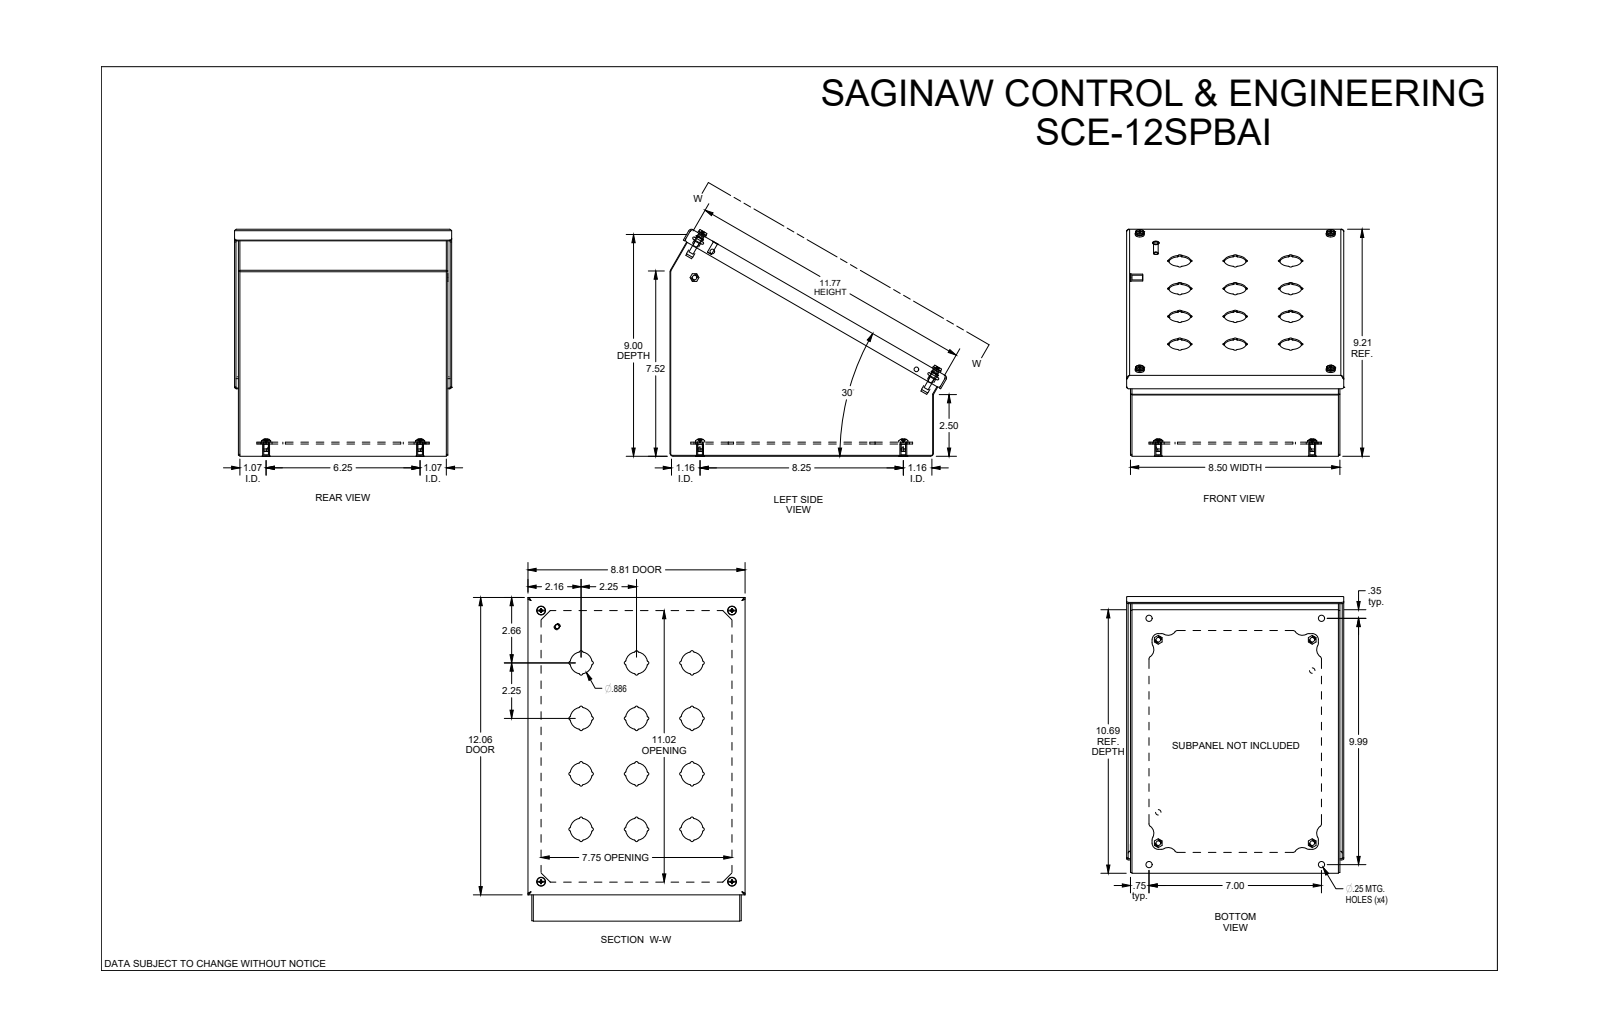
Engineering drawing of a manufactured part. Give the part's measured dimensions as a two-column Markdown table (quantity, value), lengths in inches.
| quantity | value |
| --- | --- |
| part name | SCE-12SPBAI |
| STEP written by | SolidWorks 2019 (AUTOMOTIVE_DESIGN) |
| units | inches |
| bodies | 20 solids, 765 faces (254 planar, 443 cylindrical, 68 other) |
| overall size | 11.245 × 9.233 × 8.813 |
| volume | 33.25 in³ |
| surface area | 1 091 in² |
| round holes (diameter × count) | 0.25 × 12, 0.19 × 9, 0.22 × 4, 0.266 × 4, 0.281 × 4, 0.317 × 4, 0.187 × 2, 0.218 × 2, 0.193 × 1 |
| round bosses / shafts (diameter × count) | 0.292 × 6, 0.28 × 5, 0.362 × 4, 0.34 × 4, 0.27 × 4, 0.26 × 4, 0.256 × 1, 0.188 × 1 |
| partial cylindrical surfaces (radius × count) | 0.04 × 105, 0.062 × 48, 0.03 × 14, 0.06 × 14, 0.25 × 12, 0.443 × 12, 0.01 × 8, 0.115 × 8 |
| main face-to-face distances | 0.06, 8.5, 0.06, 8.44, 8.56, 0.496, 0.436, 0.075, 0.511, 0.571 |
| hole center spacings | 7.75, 11, 11.016, 13.456, 0.947, 6.682, 7, 7.75 |
